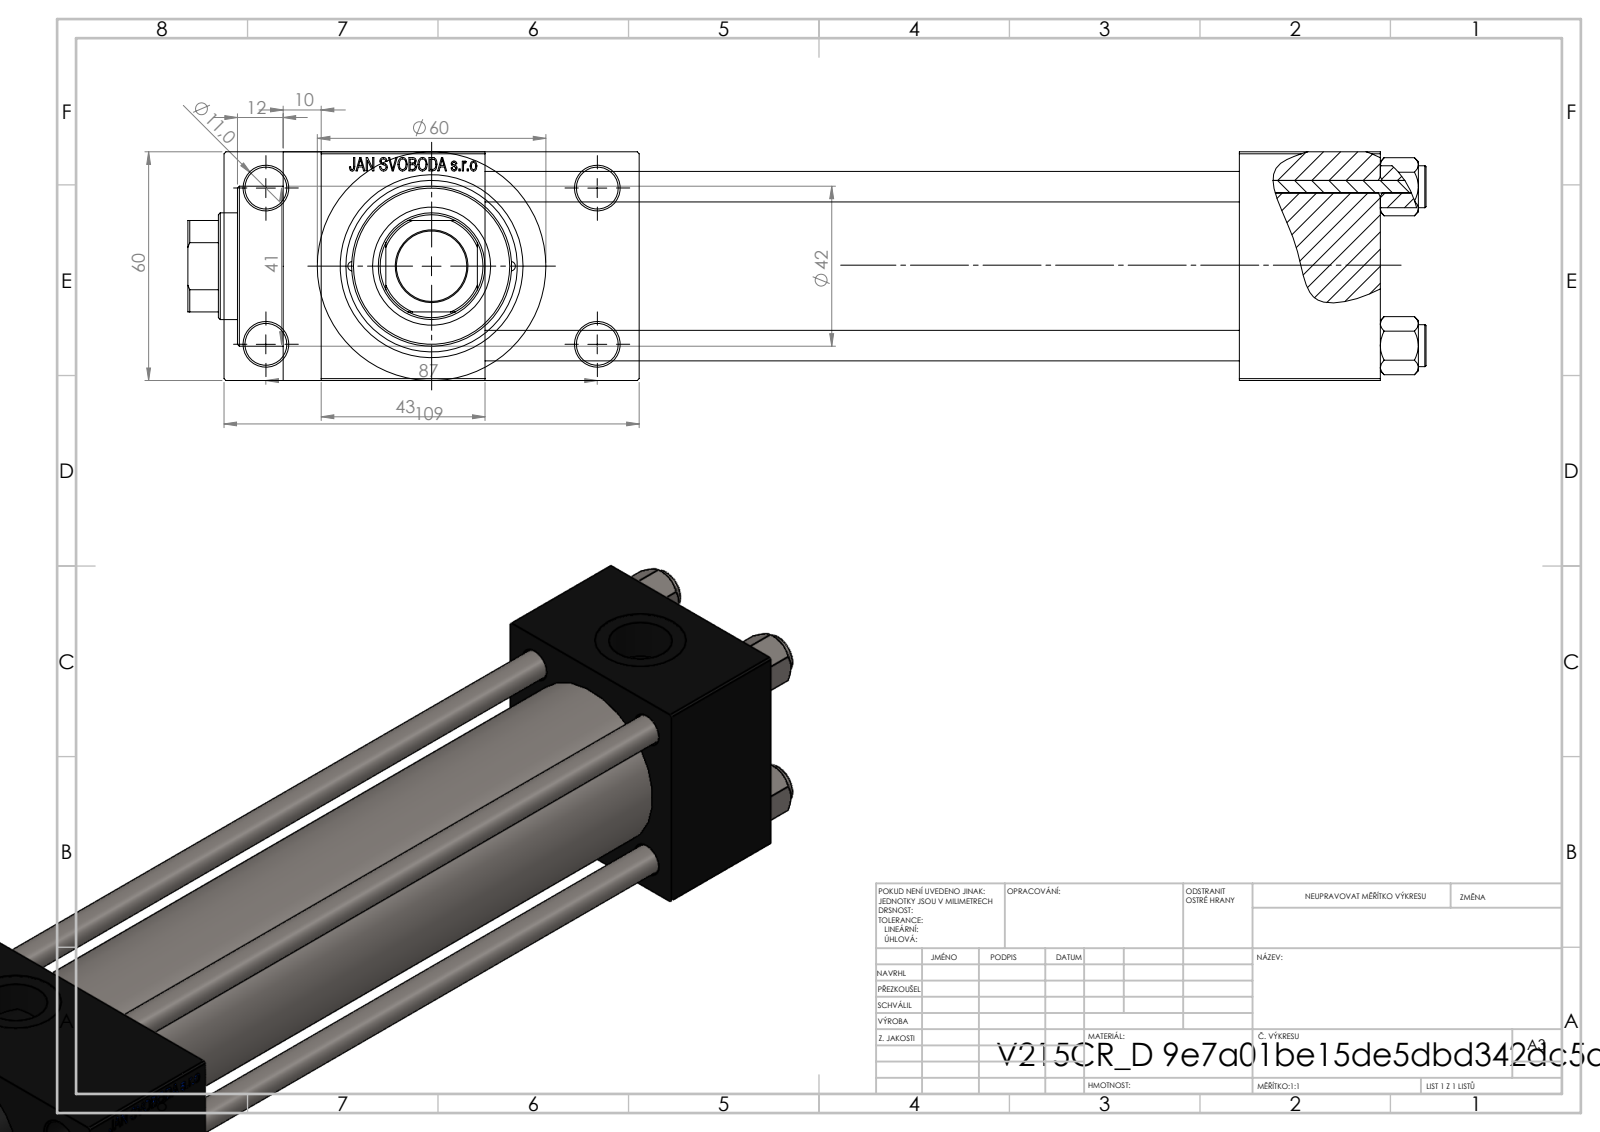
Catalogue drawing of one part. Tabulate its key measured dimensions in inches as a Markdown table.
| quantity | value |
| --- | --- |
| part name | NUT_M5_D; V215CR_D_Body; V215CR_D_TYCINKA; V215CR_VCP_D (+1 more) |
| STEP written by | SolidWorks 2019 (CONFIG_CONTROL_DESIGN) |
| units | inches |
| bodies | 11 solids, 1115 faces (502 planar, 93 cylindrical, 520 other) |
| overall size | 12.795 × 4.291 × 2.362 |
| volume | 43.02 in³ |
| surface area | 297.6 in² |
| round holes (diameter × count) | 0.315 × 4, 0.433 × 4, 0.098 × 2, 0.276 × 2, 0.656 × 2, 0.945 × 2, 0.728 × 1, 1.102 × 1, 1.22 × 1, 1.575 × 1, 1.772 × 1 |
| round bosses / shafts (diameter × count) | 0.433 × 4, 2.362 × 1, 1.811 × 1, 1.654 × 1 |
| partial cylindrical surfaces (radius × count) | 0.531 × 1 |
| main face-to-face distances | 2.362, 0.965, 3.327, 7.795, 1.457, 9.252, 10.945, 9.488, 1.693, 4.291 |
| hole center spacings | 0.821, 0.892, 1.161, 1.206, 1.642, 1.832, 1.856, 1.893 |
